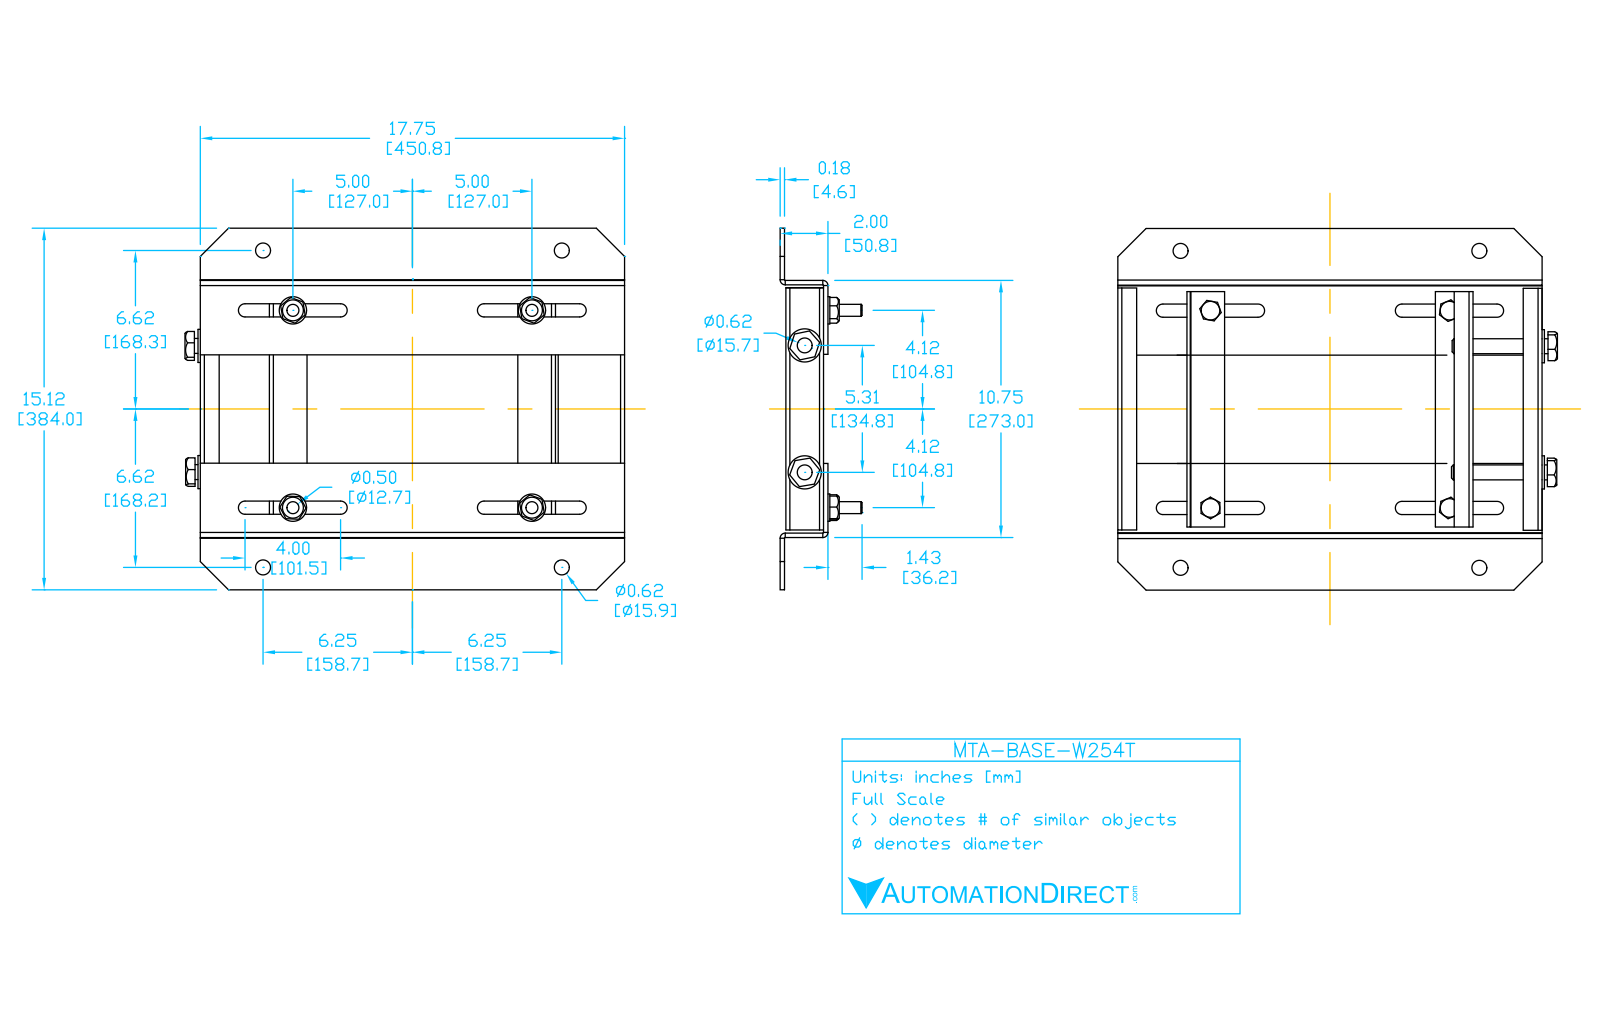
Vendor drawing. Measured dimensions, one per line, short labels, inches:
name: W254T
written by: SolidWorks 2017 (AUTOMOTIVE_DESIGN)
unit: in
bodies: 26 solids, 398 faces (224 planar, 110 cylindrical, 64 other)
size: 18.391 × 15.12 × 3.427
volume: 68.74 in³; area: 837.4 in²
holes: 4× ⌀0.5, 4× ⌀0.504, 4× ⌀0.531, 4× ⌀0.625, 2× ⌀0.625, 2× ⌀0.65, 2× ⌀0.748
bosses: 4× ⌀1.142, 2× ⌀1.386
rounds: 11× R0.029, 8× R0.276, 7× R0.167, 4× R0.214
face distances: 0.185, 1.815, 0.138, 1.63, 2, 10.565, 1.437, 0.323, 1.492, 1.677
hole spacings: 8.25, 10, 12.5, 12.964, 13.25, 18.216, 2.604, 2.609
